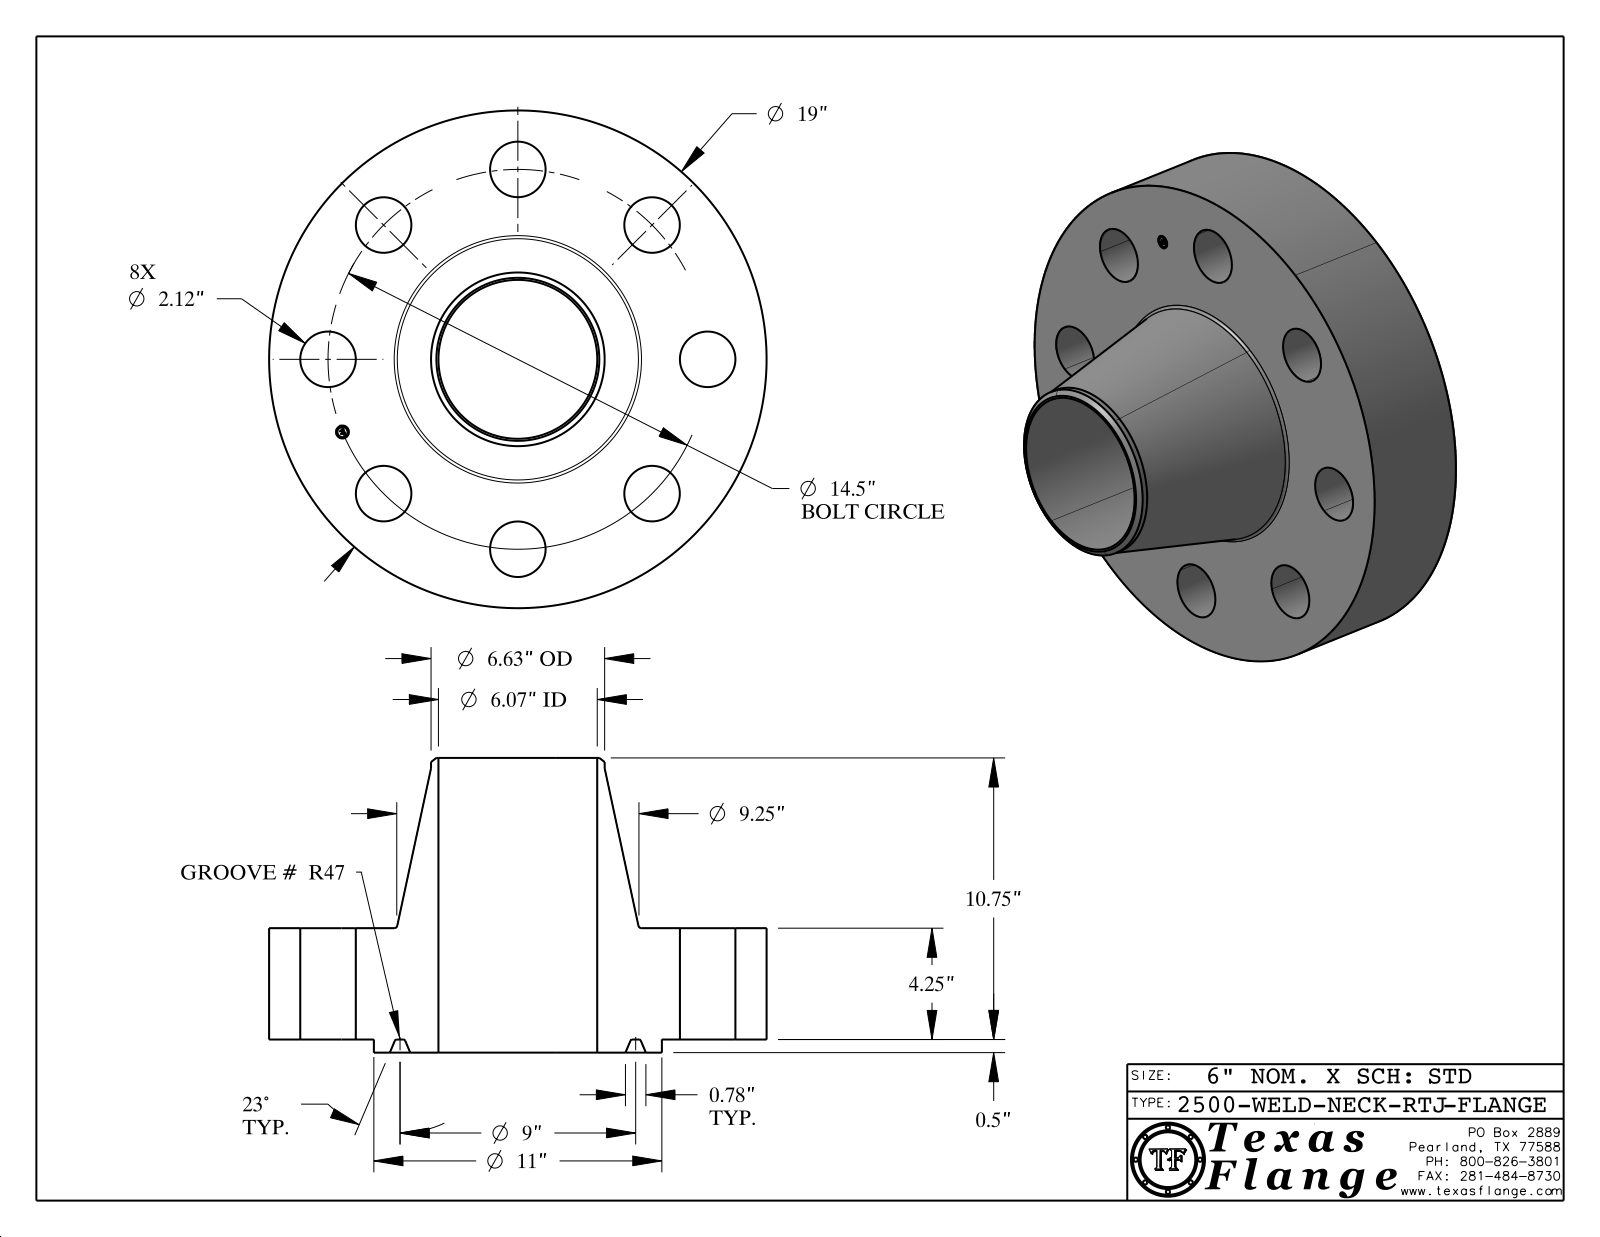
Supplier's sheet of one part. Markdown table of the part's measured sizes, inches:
| quantity | value |
| --- | --- |
| part name | 2500-WELD-NECK-RTJ |
| STEP written by | CATIA V5 STEP AP214 (AUTOMOTIVE_DESIGN) |
| units | inches |
| bodies | 1 solid, 429 faces (371 planar, 44 cylindrical, 14 other) |
| overall size | 19 × 19 × 11.25 |
| volume | 1 118 in³ |
| surface area | 1 311 in² |
| round holes (diameter × count) | 2.12 × 8, 0.495 × 1, 6.065 × 1 |
| round bosses / shafts (diameter × count) | 0.03 × 8, 19 × 1, 11 × 1, 6.63 × 1, 0.39 × 1 |
| main face-to-face distances | 4.25, 0.5, 4.75, 11.25, 10.75, 6.5, 0.015, 4.735, 4.235, 6.515 |
| hole center spacings | 5.549, 13.396, 7.25, 7.25, 10.253, 10.253, 2.829, 14.221 |
